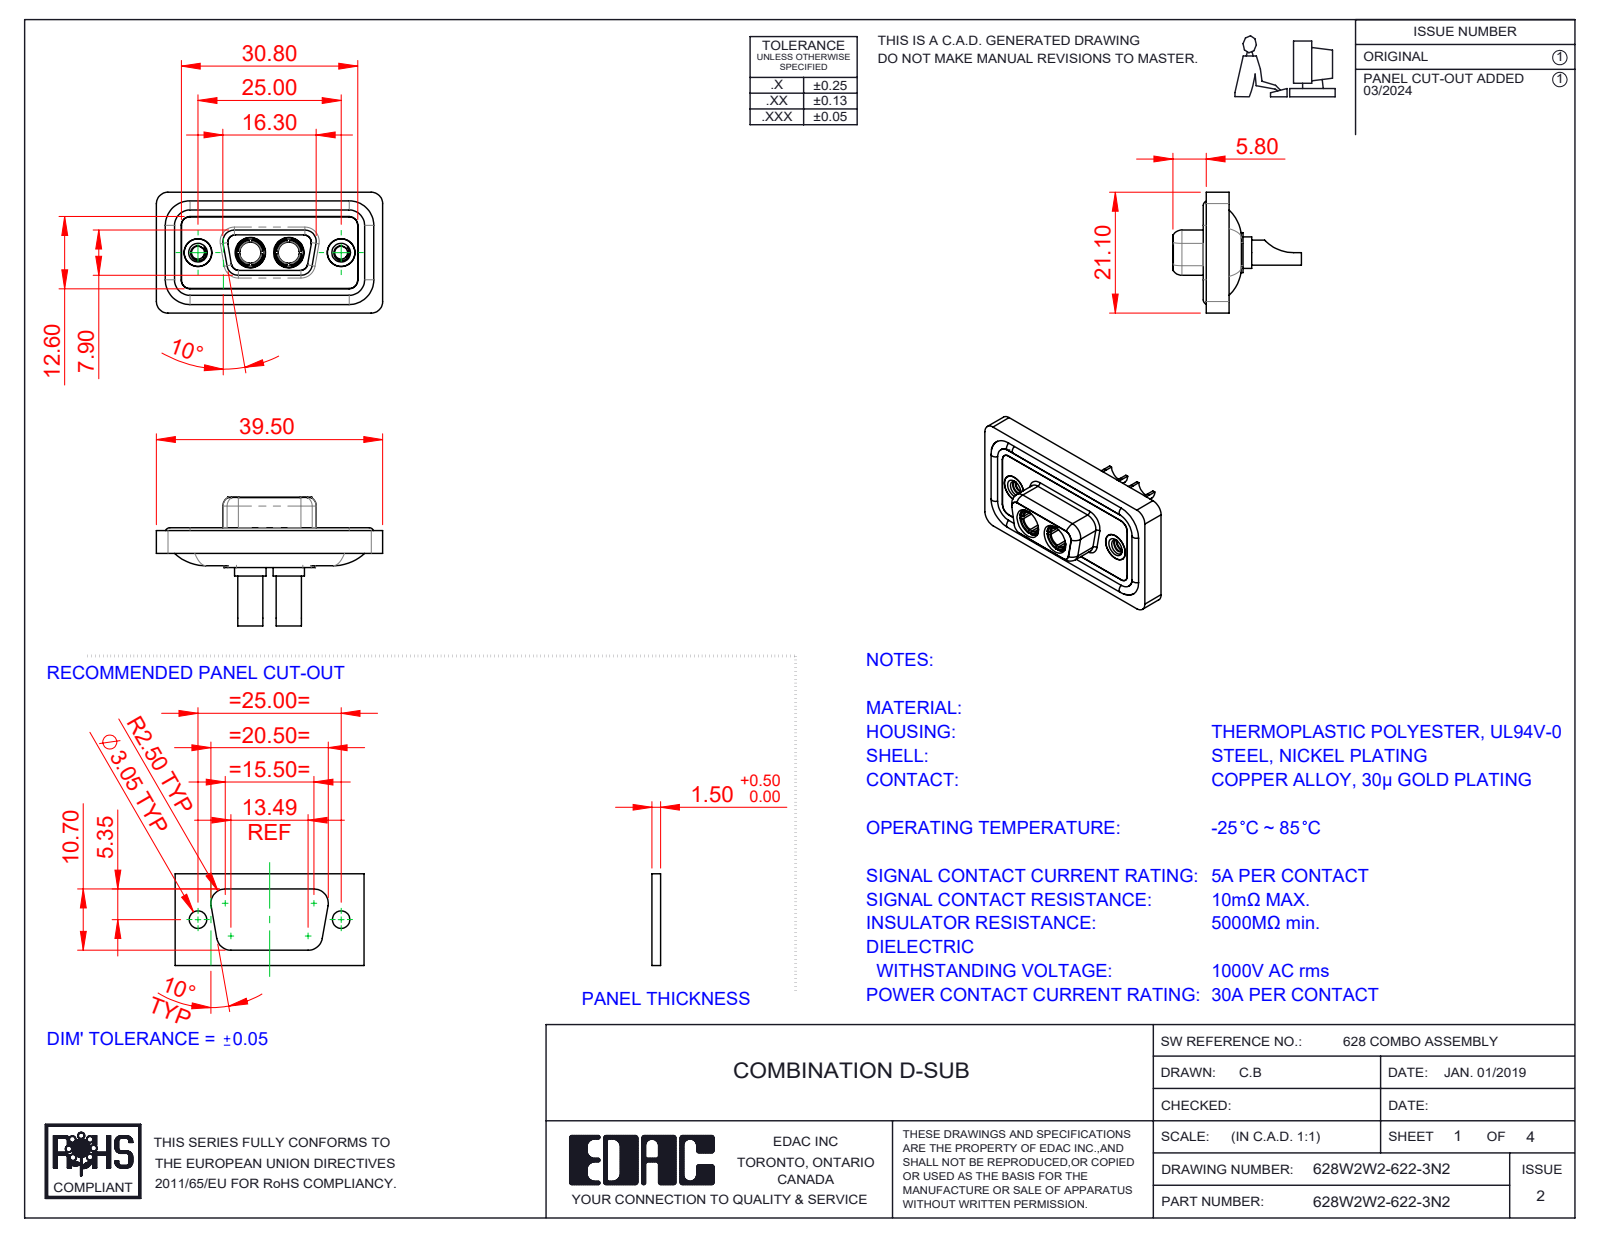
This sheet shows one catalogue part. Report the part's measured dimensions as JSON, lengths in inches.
{"part_name": "628Combo Shell Front_09 Contacts; 628Combo Housing_2W2; Power Socket_30A SC; 628W2W2-622-3N2 (+3 more)", "step_written_by": "SolidWorks 2023 (CONFIG_CONTROL_DESIGN)", "units": "inches", "bodies": {"solids": 11, "faces": 546, "planar": 169, "cylindrical": 240, "other": 137}, "overall_size": [1.555, 0.884, 0.831], "volume_in3": 0.291, "surface_area_in2": 12.17, "round_holes": [[0.191, 4], [0.089, 2], [0.138, 2], [0.146, 2], [0.157, 2], [0.159, 2], [0.197, 2], [0.209, 2]], "round_bosses_or_shafts": [[0.063, 4], [0.217, 2], [0.205, 2], [0.195, 2], [0.195, 2], [0.189, 2], [0.187, 2], [0.173, 2]], "partial_cylinders_radius": [[0.059, 22], [0.079, 18], [0.053, 8], [0.063, 8], [0.01, 4], [0.02, 4], [0.024, 4], [0.026, 4]], "face_to_face_distances": [0.016, 0.043, 0.114, 0.071, 0.02, 0.063, 0.222, 0.293, 0.211, 0.122], "hole_center_spacings": [0.36, 0.624, 0.265, 0.984]}
